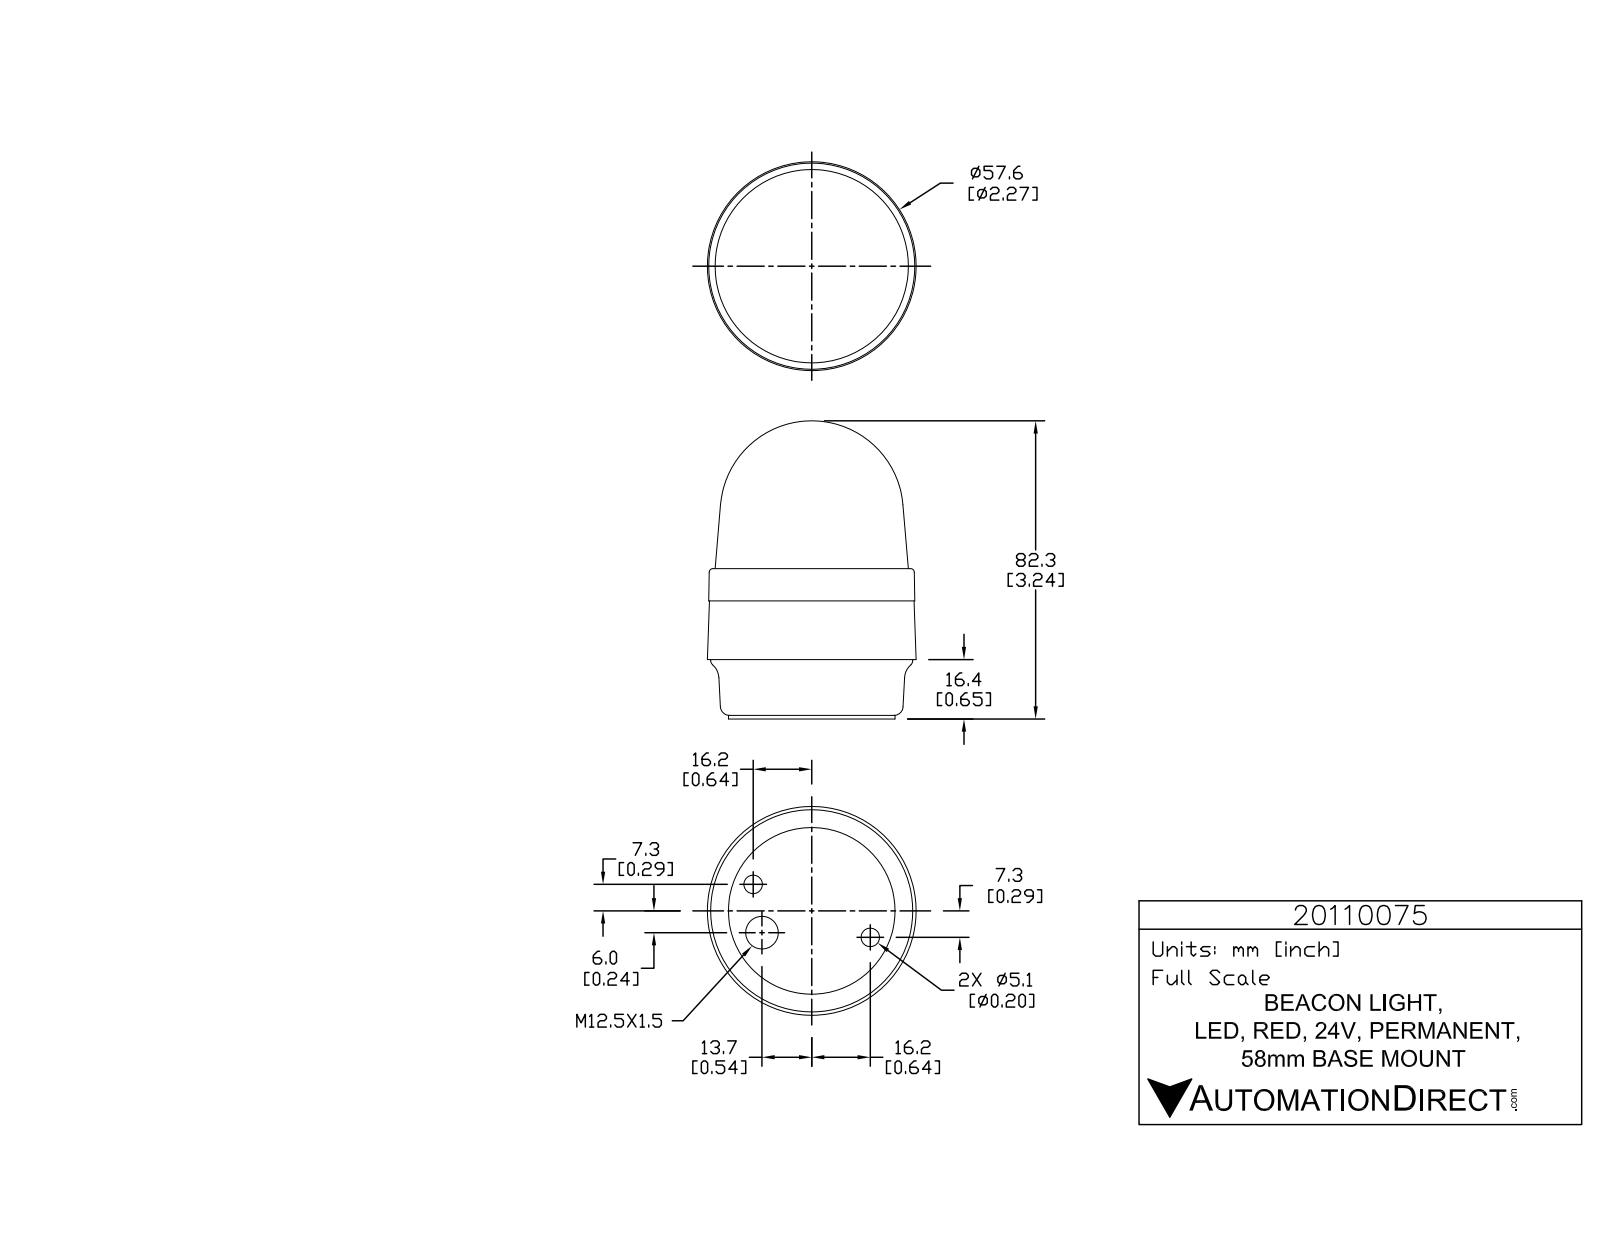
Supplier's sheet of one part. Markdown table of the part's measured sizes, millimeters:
| quantity | value |
| --- | --- |
| part name | 20110075 |
| STEP written by | SolidWorks 2015 (AUTOMOTIVE_DESIGN) |
| units | millimeters |
| bodies | 1 solid, 763 faces (527 planar, 145 cylindrical, 91 other) |
| overall size | 82.3 × 57.63 × 57.63 |
| volume | 164 395 mm³ |
| surface area | 16 261 mm² |
| round holes (diameter × count) | 0.99 × 3, 5.11 × 2, 9 × 1 |
| round bosses / shafts (diameter × count) | 5.74 × 3, 1.43 × 3, 55.8 × 1, 46 × 1 |
| partial cylindrical surfaces (radius × count) | 0.2 × 6, 0.21 × 6, 0.21 × 6, 3.32 × 6, 0.1 × 3, 0.12 × 3, 0.19 × 3, 0.2 × 3 |
| main face-to-face distances | 16.4, 1, 15.4, 41.5, 40.5, 25.1, 32.6, 31.6, 16.2, 8.9 |
| hole center spacings | 13.56, 29.94, 35.5 |
